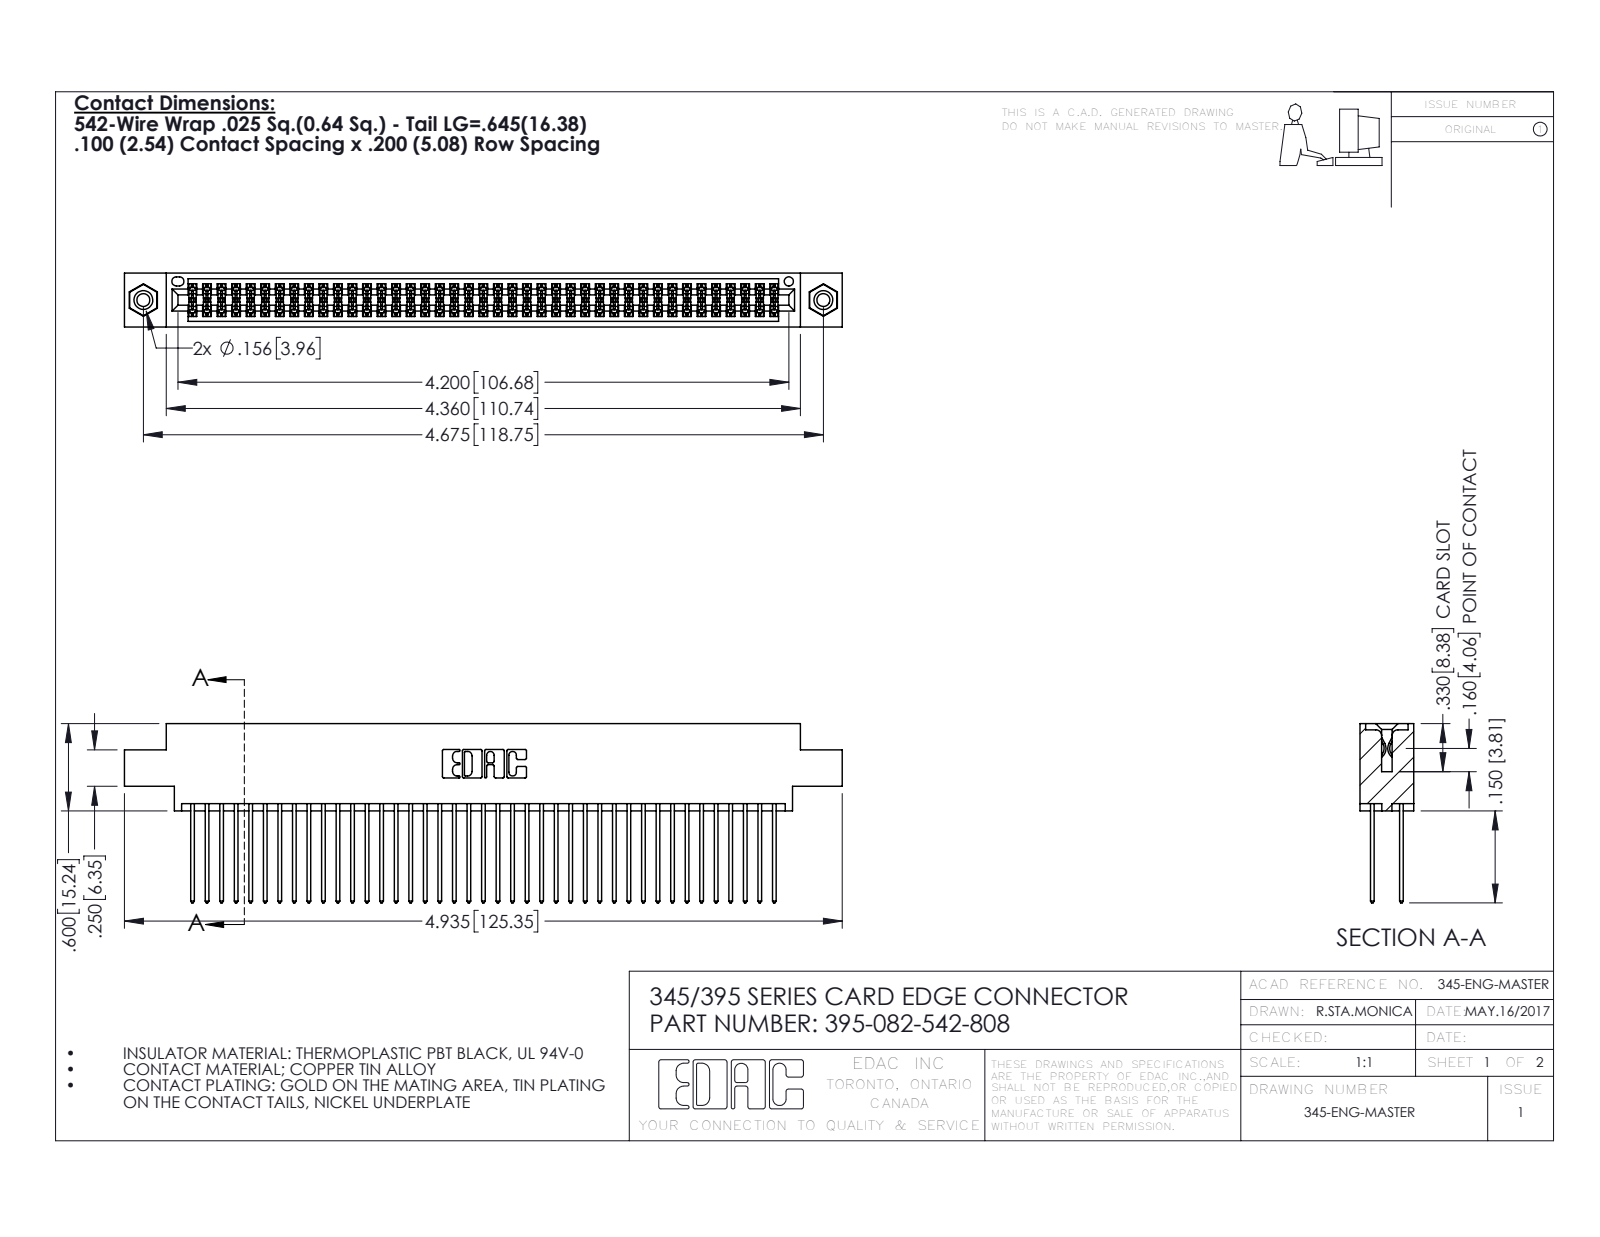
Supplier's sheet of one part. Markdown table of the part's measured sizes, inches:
| quantity | value |
| --- | --- |
| part name | 345-250-001_345-250-003-102; 345 Part_0.170 Offset - 0.156 Dia-TI; 395-082-542-808; 345-292-001_345-293-142 |
| STEP written by | SolidWorks 2016 (CONFIG_CONTROL_DESIGN) |
| units | inches |
| bodies | 85 solids, 4290 faces (2822 planar, 1452 cylindrical, 16 other) |
| overall size | 4.935 × 1.232 × 0.37 |
| volume | 0.759 in³ |
| surface area | 31.46 in² |
| round holes (diameter × count) | 0.089 × 2, 0.125 × 2, 0.156 × 2, 0.064 × 1 |
| round bosses / shafts (diameter × count) | 0.155 × 2 |
| partial cylindrical surfaces (radius × count) | 0.006 × 123, 0.01 × 82, 0.01 × 22, 0.007 × 6, 0.031 × 6, 0.026 × 3, 0.014 × 2, 0.019 × 2 |
| main face-to-face distances | 0.072, 0.298, 0.2, 0.098, 0.272, 0.025, 0.37, 0.225, 0.175, 0.149 |
| hole center spacings | 0.27, 4.439, 4.675 |
